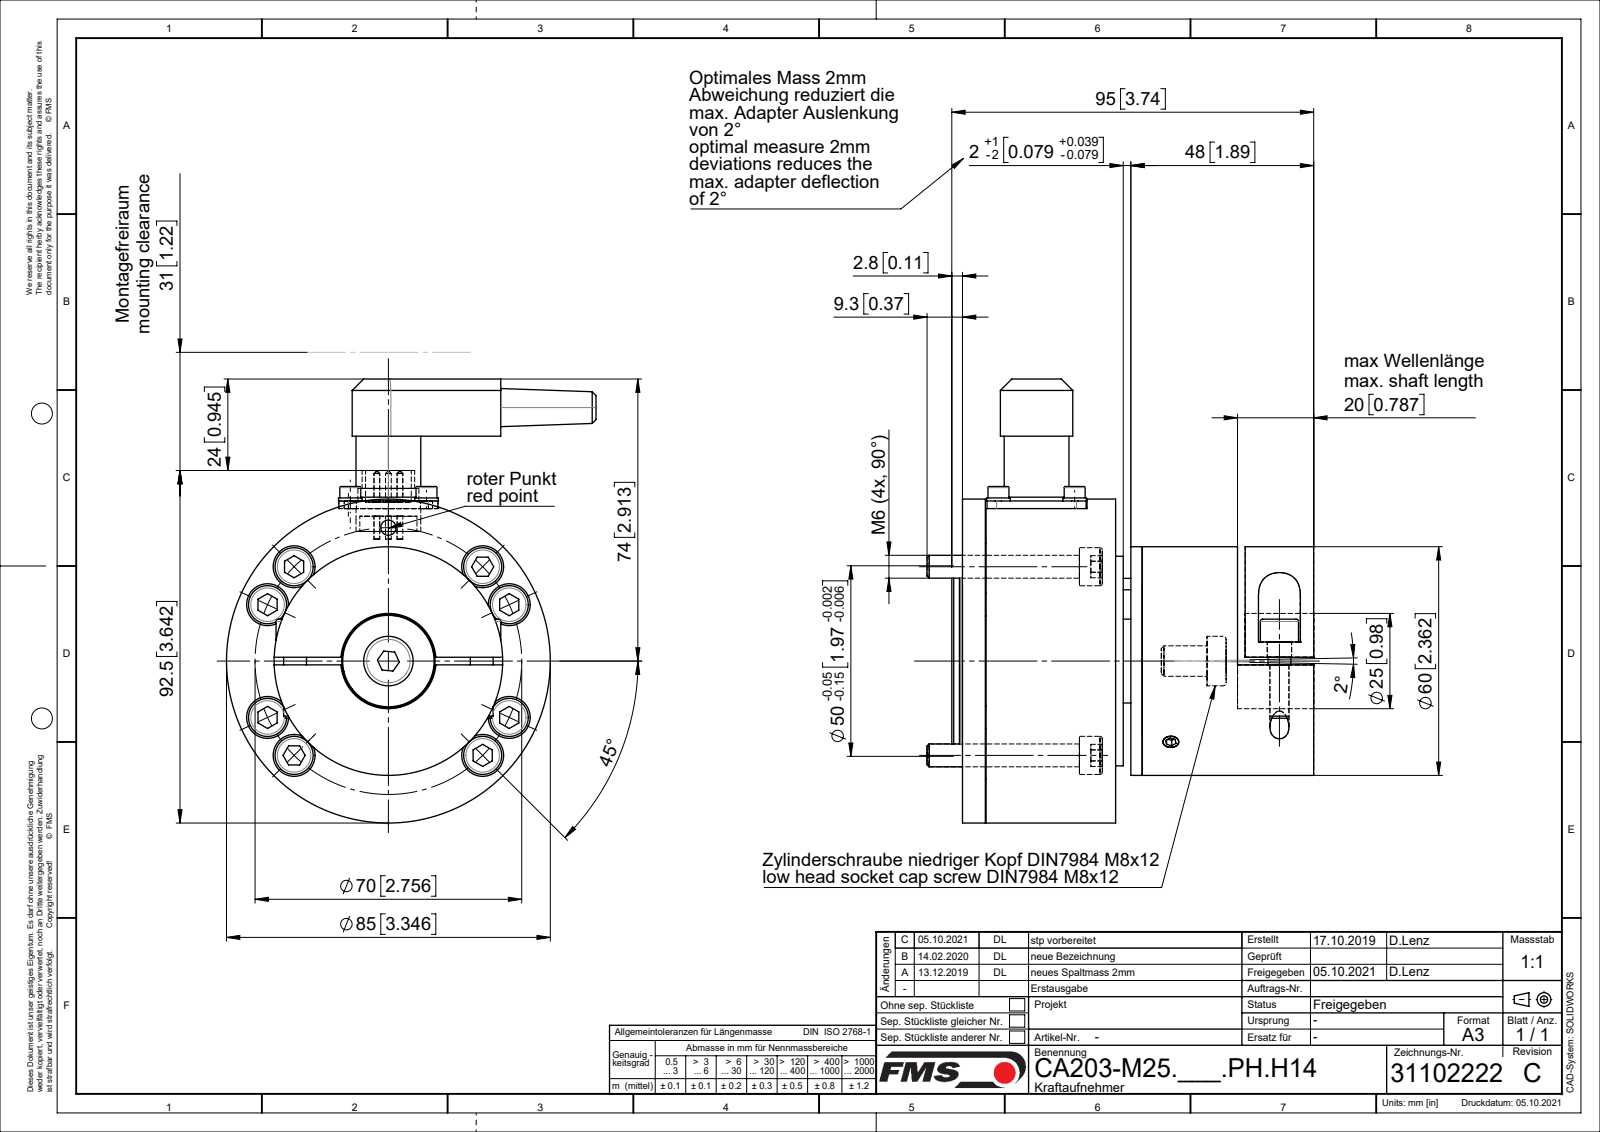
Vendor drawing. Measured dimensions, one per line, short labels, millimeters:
name: Zyl-Schr DIN7984_M8x12; 061205-3_01; Gew-Sti-I6kt-Zapfen DIN915_M5x10; Sch DIN9021_M8 (+8 more)
written by: SolidWorks 2018 (CONFIG_CONTROL_DESIGN)
unit: mm
bodies: 44 solids, 839 faces (302 planar, 339 cylindrical, 198 other)
size: 116.5 × 101.5 × 97
volume: 305 199 mm³; area: 111 888 mm²
holes: 8× ⌀2.5, 8× ⌀6.5, 8× ⌀11, 6× ⌀5, 5× ⌀2, 5× ⌀4, 4× ⌀3.1, 4× ⌀3.2, 4× ⌀3.6, 4× ⌀7, 2× ⌀6.4, 1× ⌀3
bosses: 11× ⌀6, 10× ⌀10, 8× ⌀3, 5× ⌀1.5, 4× ⌀6.2, 4× ⌀5.7, 4× ⌀5.5, 1× ⌀85
rounds: 4× R2.5, 2× R5, 2× R5.5, 1× R9.5
face distances: 2, 41, 30, 6, 45, 34, 10, 3, 50, 12
hole spacings: 35, 20, 24.78, 25.2, 32.8, 51.14, 56.46, 6
